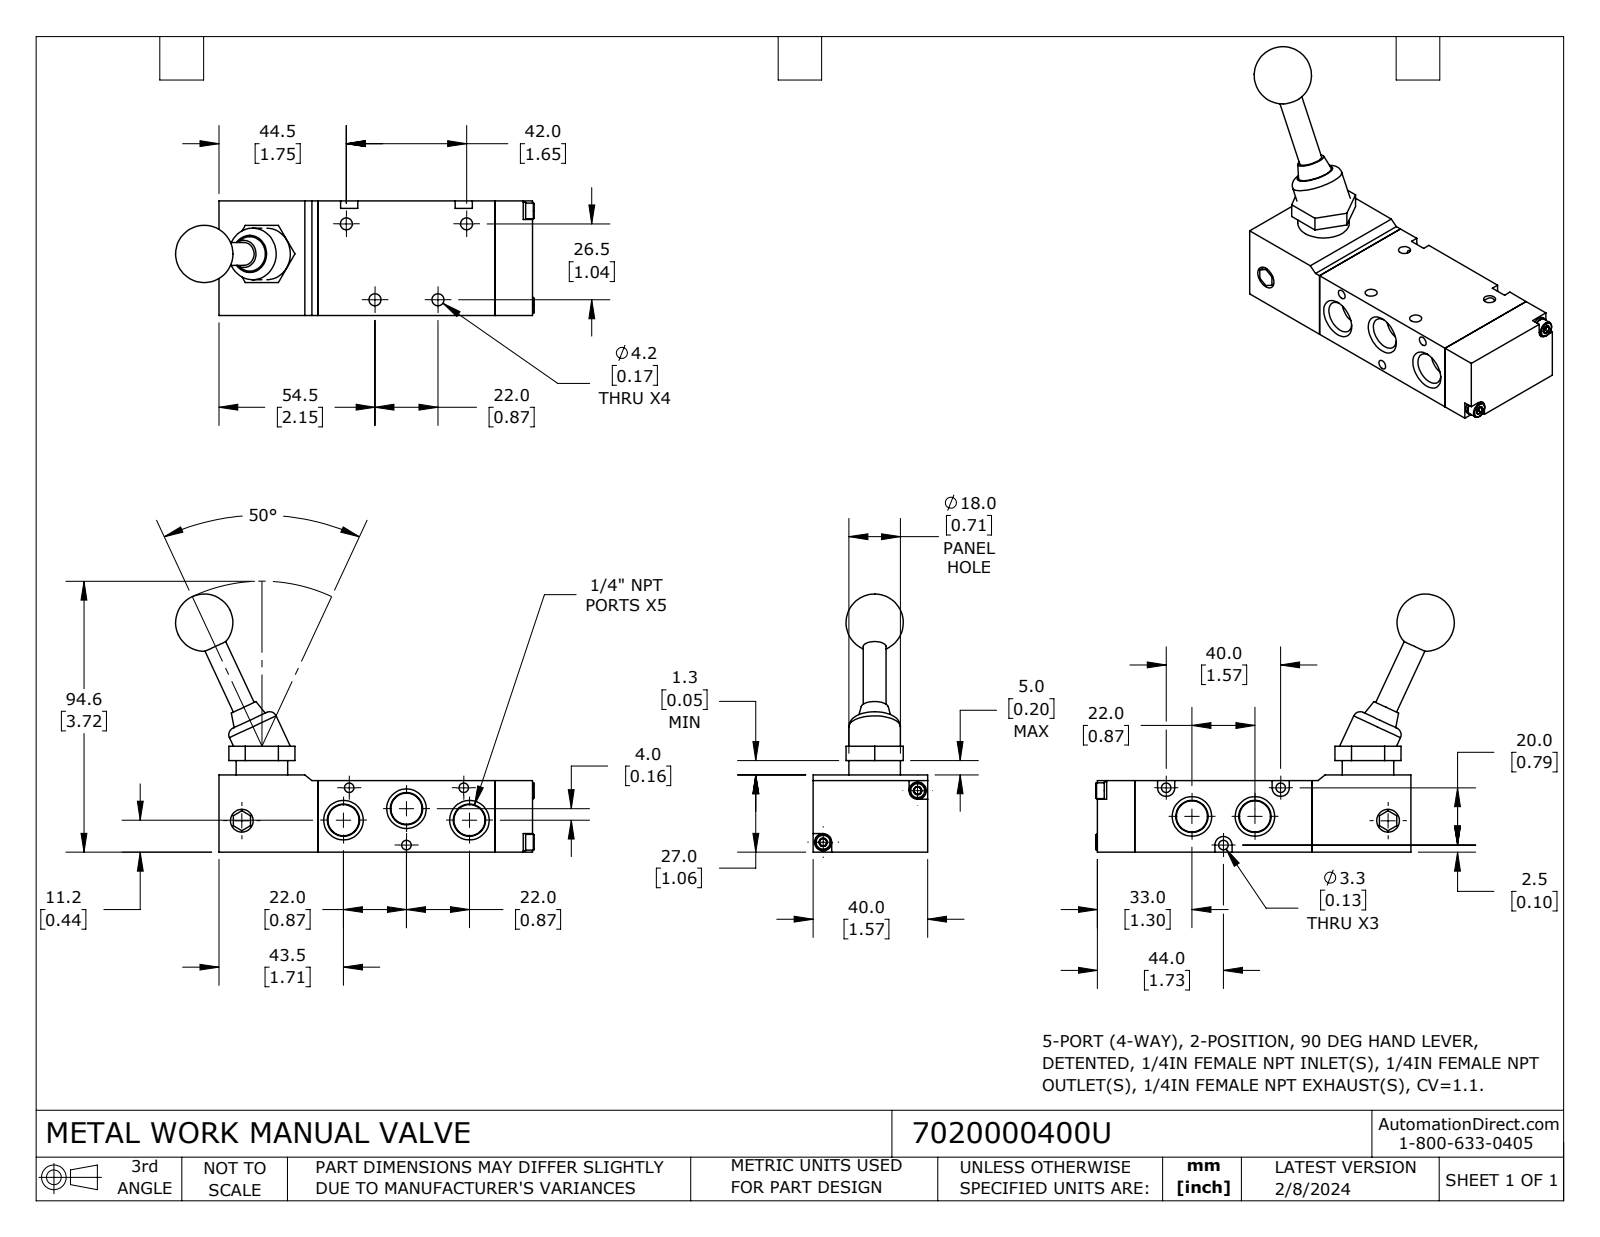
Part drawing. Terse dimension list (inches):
name: 7020000400U
written by: SolidWorks 2023 (CONFIG_CONTROL_DESIGN)
unit: in
bodies: 8 solids, 206 faces (101 planar, 51 cylindrical, 54 other)
size: 4.93 × 3.549 × 1.575
volume: 7.193 in³; area: 44.53 in²
holes: 4× ⌀0.165, 3× ⌀0.13, 2× ⌀0.118, 1× ⌀0.313
bosses: 2× ⌀0.709, 2× ⌀0.236, 2× ⌀0.217, 1× ⌀0.315
rounds: 3× R0.118
face distances: 0.984, 1.575, 2.441, 3.799, 1.358, 1.063, 0.079, 0.512, 2.953, 4.311
hole spacings: 1.113, 1.115, 1.636, 0.866, 1.48, 1.544, 1.575, 1.654
